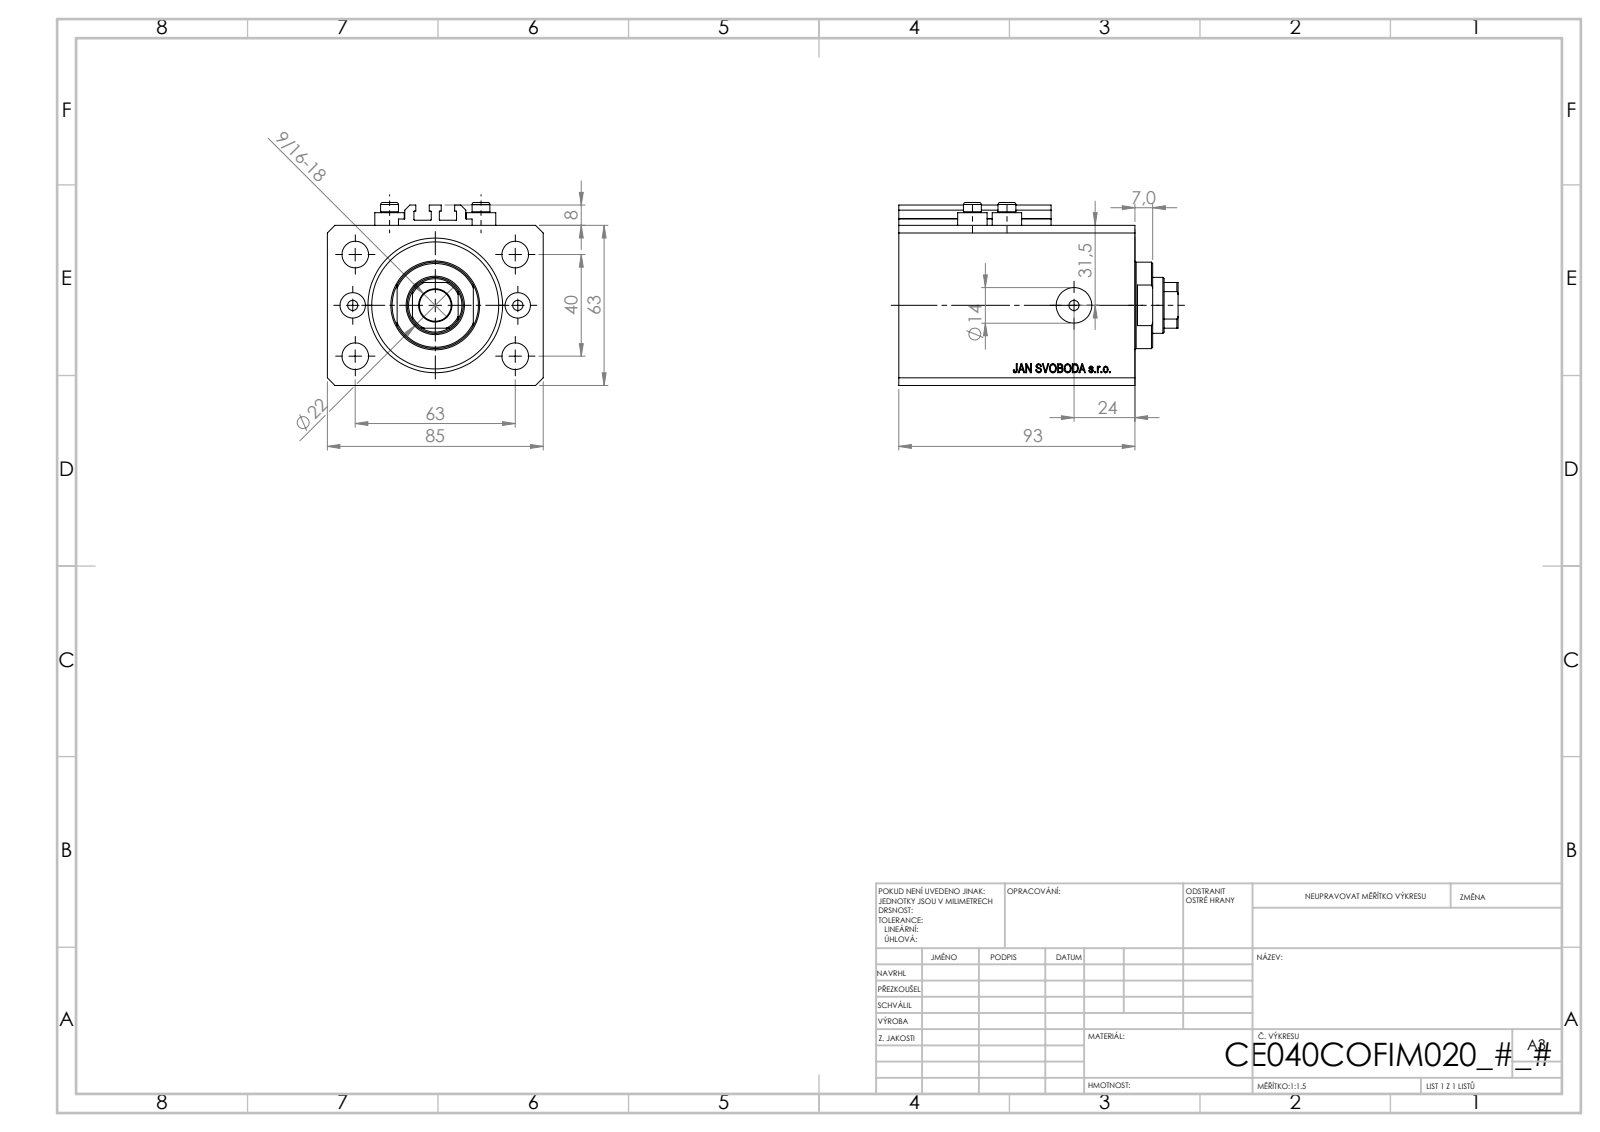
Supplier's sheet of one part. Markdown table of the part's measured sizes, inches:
| quantity | value |
| --- | --- |
| part name | ALLEN BOLT V250CE; V250CE_C_VCP; V250CE_C_Body; V250CE_VC_C |
| STEP written by | SolidWorks 2019 (CONFIG_CONTROL_DESIGN) |
| units | inches |
| bodies | 8 solids, 1034 faces (504 planar, 86 cylindrical, 444 other) |
| overall size | 4.331 × 3.346 × 2.835 |
| volume | 28.08 in³ |
| surface area | 142.9 in² |
| round holes (diameter × count) | 0.157 × 8, 0.413 × 4, 0.394 × 2, 0.551 × 2, 0.492 × 1, 0.866 × 1, 1.575 × 1, 2.087 × 1 |
| round bosses / shafts (diameter × count) | 0.457 × 4, 0.276 × 4, 1.339 × 1 |
| partial cylindrical surfaces (radius × count) | 0.008 × 10, 0.413 × 1 |
| main face-to-face distances | 2.48, 3.346, 3.661, 0.669, 2.992, 0.449, 2.543, 3.213, 0.118, 0.394 |
| hole center spacings | 0.788, 1.469, 2.64, 0.535, 1.28, 1.417, 1.515, 1.575 |
